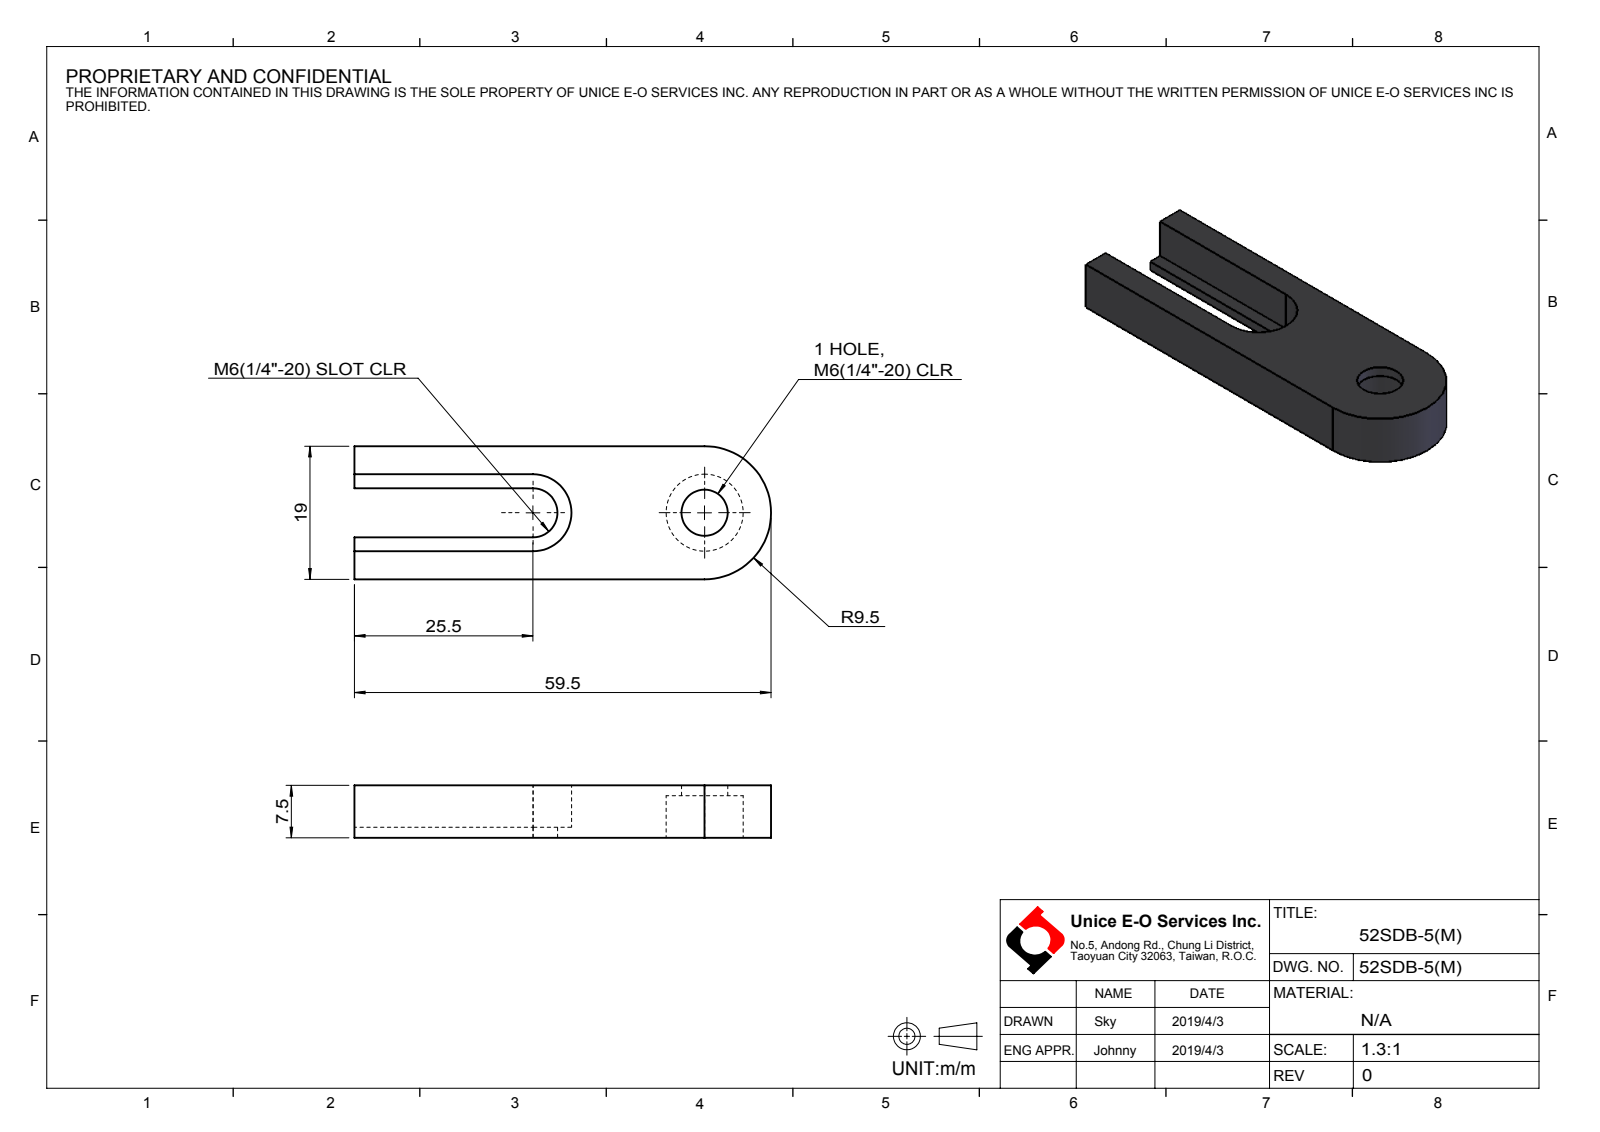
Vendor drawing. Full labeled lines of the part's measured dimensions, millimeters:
Part name (STEP PRODUCT): 52SDB-5(M)
STEP written by: SolidWorks 2016 (CONFIG_CONTROL_DESIGN)
Units: millimetres
Bodies: 1 solid, 19 faces (12 planar, 7 cylindrical, 0 other)
Overall size (bounding box): 59.5 × 19 × 7.5
Volume: 5 302 mm³ · Surface area: 3 501 mm²
Round holes (diameter × count): ⌀6.6 ×1, ⌀11 ×1
Partial cylindrical surfaces — rounded edges, fillets, slot ends (radius × count): R3.5 ×1, R5.5 ×1, R9.5 ×1
Main face-to-face distances: 7.5, 19, 4, 15, 6, 1.5, 11, 13, 2, 9
